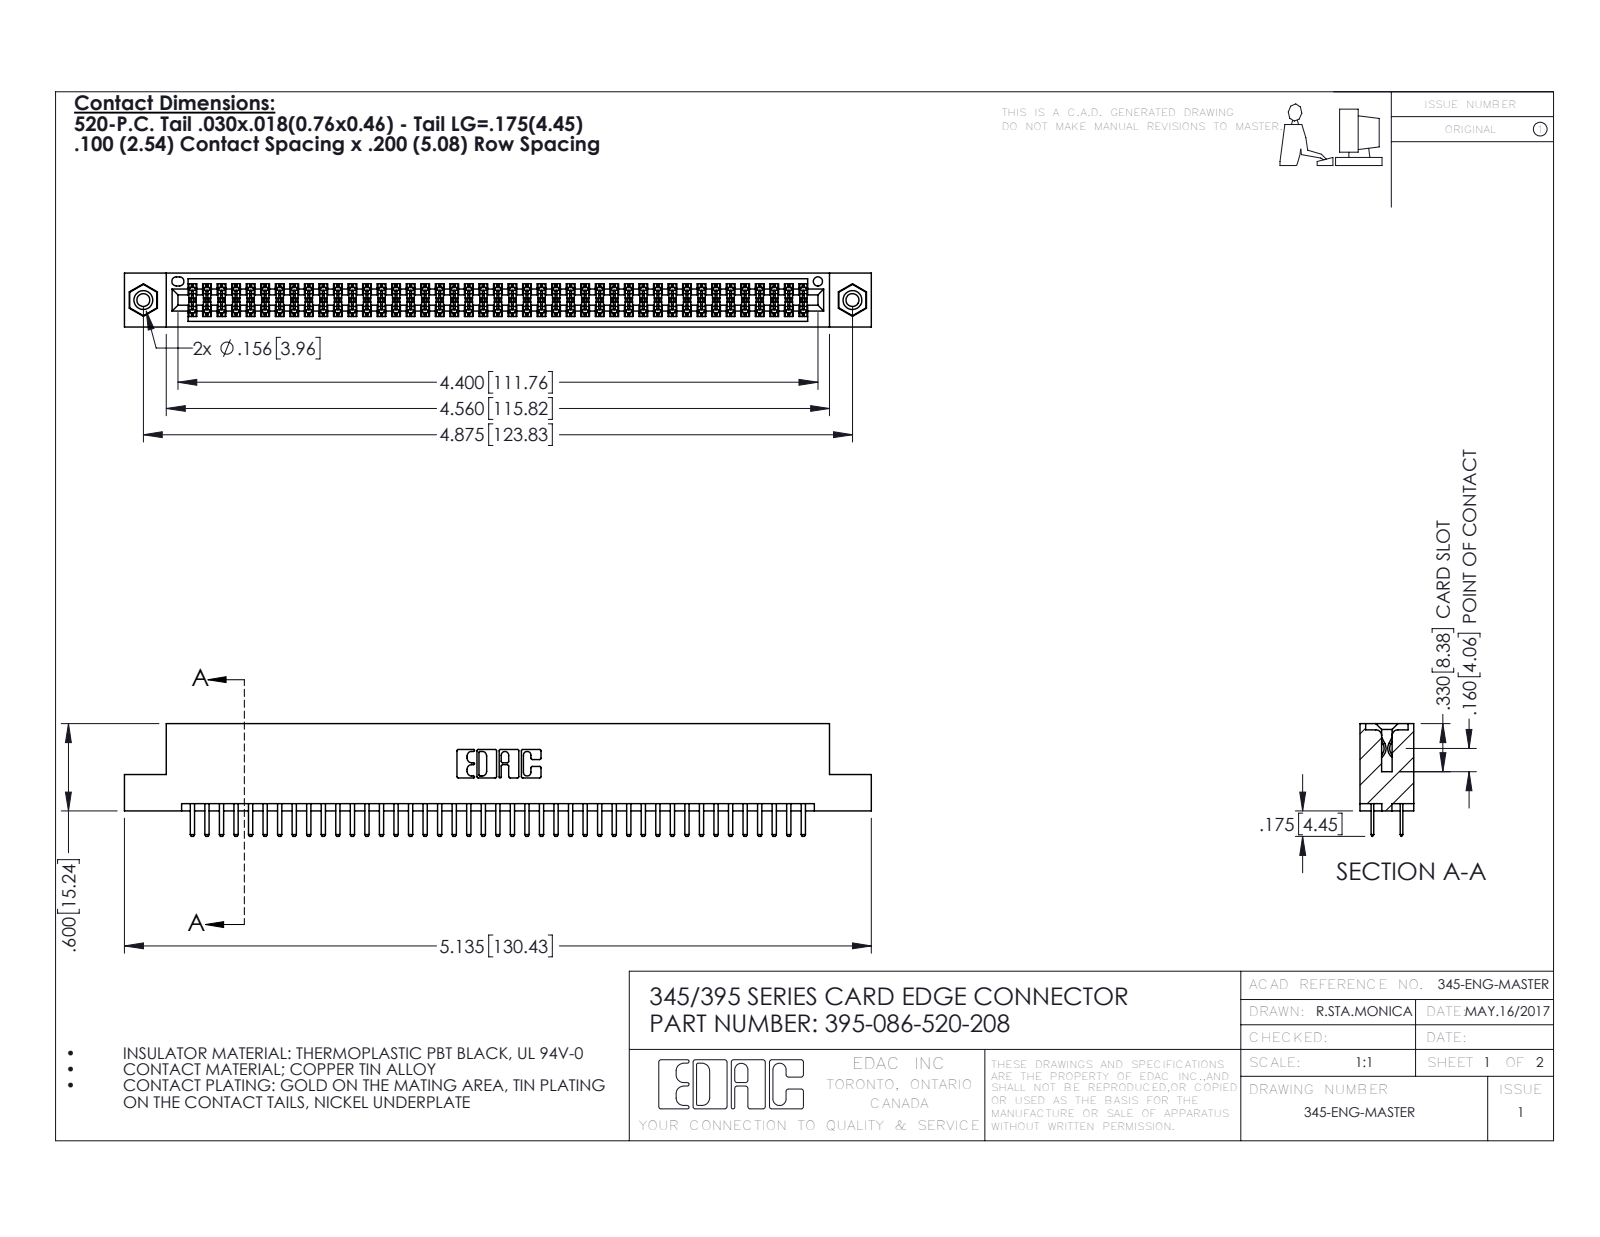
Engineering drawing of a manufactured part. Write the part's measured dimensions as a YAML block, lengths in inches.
part_name: "395-086-520-208; 345-250-001_345-250-003-102; 345-292-001_345-293-120; 345 Part_Flush Mounting Lugs - 0.156 Dia-TI"
step_written_by: "SolidWorks 2016 (CONFIG_CONTROL_DESIGN)"
units: inches
bodies: {solids: 89, faces: 4830, planar: 3122, cylindrical: 1692, other: 16}
overall_size: [5.135, 0.775, 0.37]
volume: 0.771
surface_area: 28.87
round_holes:
  - {diameter: 0.089, count: 2}
  - {diameter: 0.125, count: 2}
  - {diameter: 0.156, count: 2}
  - {diameter: 0.064, count: 1}
round_bosses_or_shafts:
  - {diameter: 0.155, count: 2}
partial_cylinders:
  - {radius: 0.006, count: 129}
  - {radius: 0.01, count: 90}
  - {radius: 0.01, count: 22}
  - {radius: 0.007, count: 6}
  - {radius: 0.031, count: 6}
  - {radius: 0.026, count: 3}
  - {radius: 0.014, count: 2}
  - {radius: 0.019, count: 2}
face_to_face_distances: [0.072, 0.298, 0.2, 0.37, 0.098, 0.272, 0.025, 0.225, 0.022, 0.072]
hole_center_spacings: [0.27, 4.639, 4.875]
